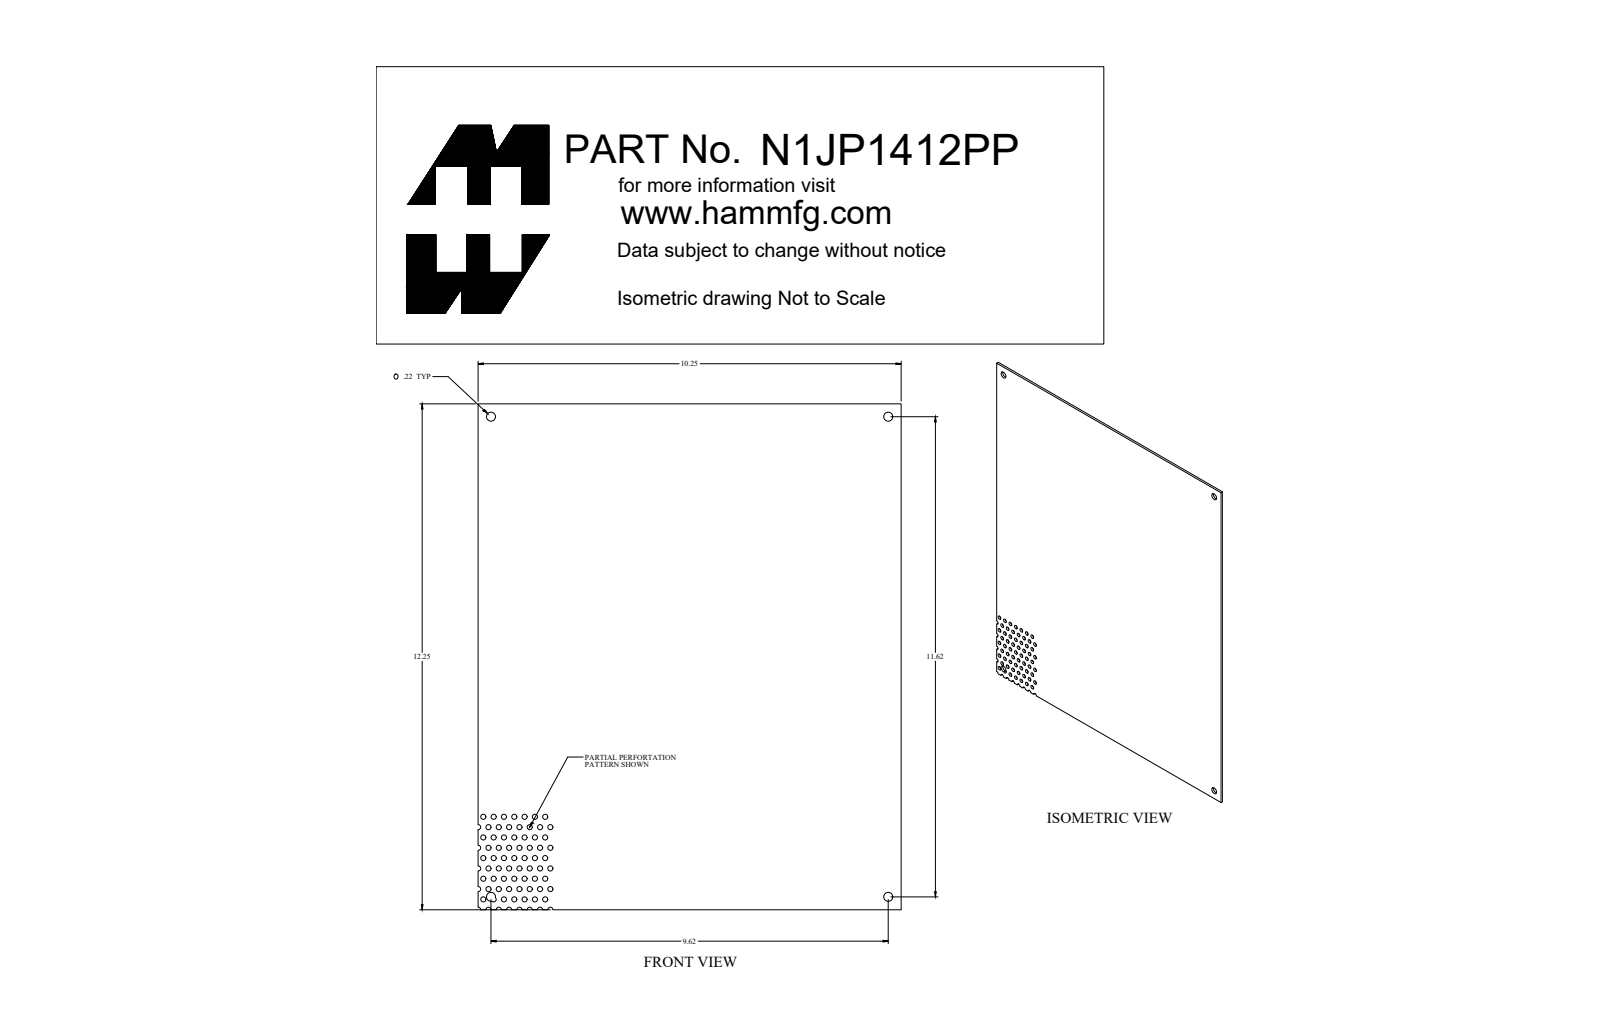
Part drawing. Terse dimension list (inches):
name: N1JP1412PP
written by: SolidWorks 2018 (AUTOMOTIVE_DESIGN)
unit: in
bodies: 1 solid, 168 faces (17 planar, 151 cylindrical, 0 other)
size: 12.25 × 10.25 × 0.072
volume: 8.97 in³; area: 254.4 in²
holes: 57× ⌀0.125, 5× ⌀0.125, 4× ⌀0.218
rounds: 8× R0.063, 5× R0.062
face distances: 0.072, 10.25, 12.25
hole spacings: 0.25, 0.5, 1, 0.28, 0.75, 1.118, 0.45, 0.761
